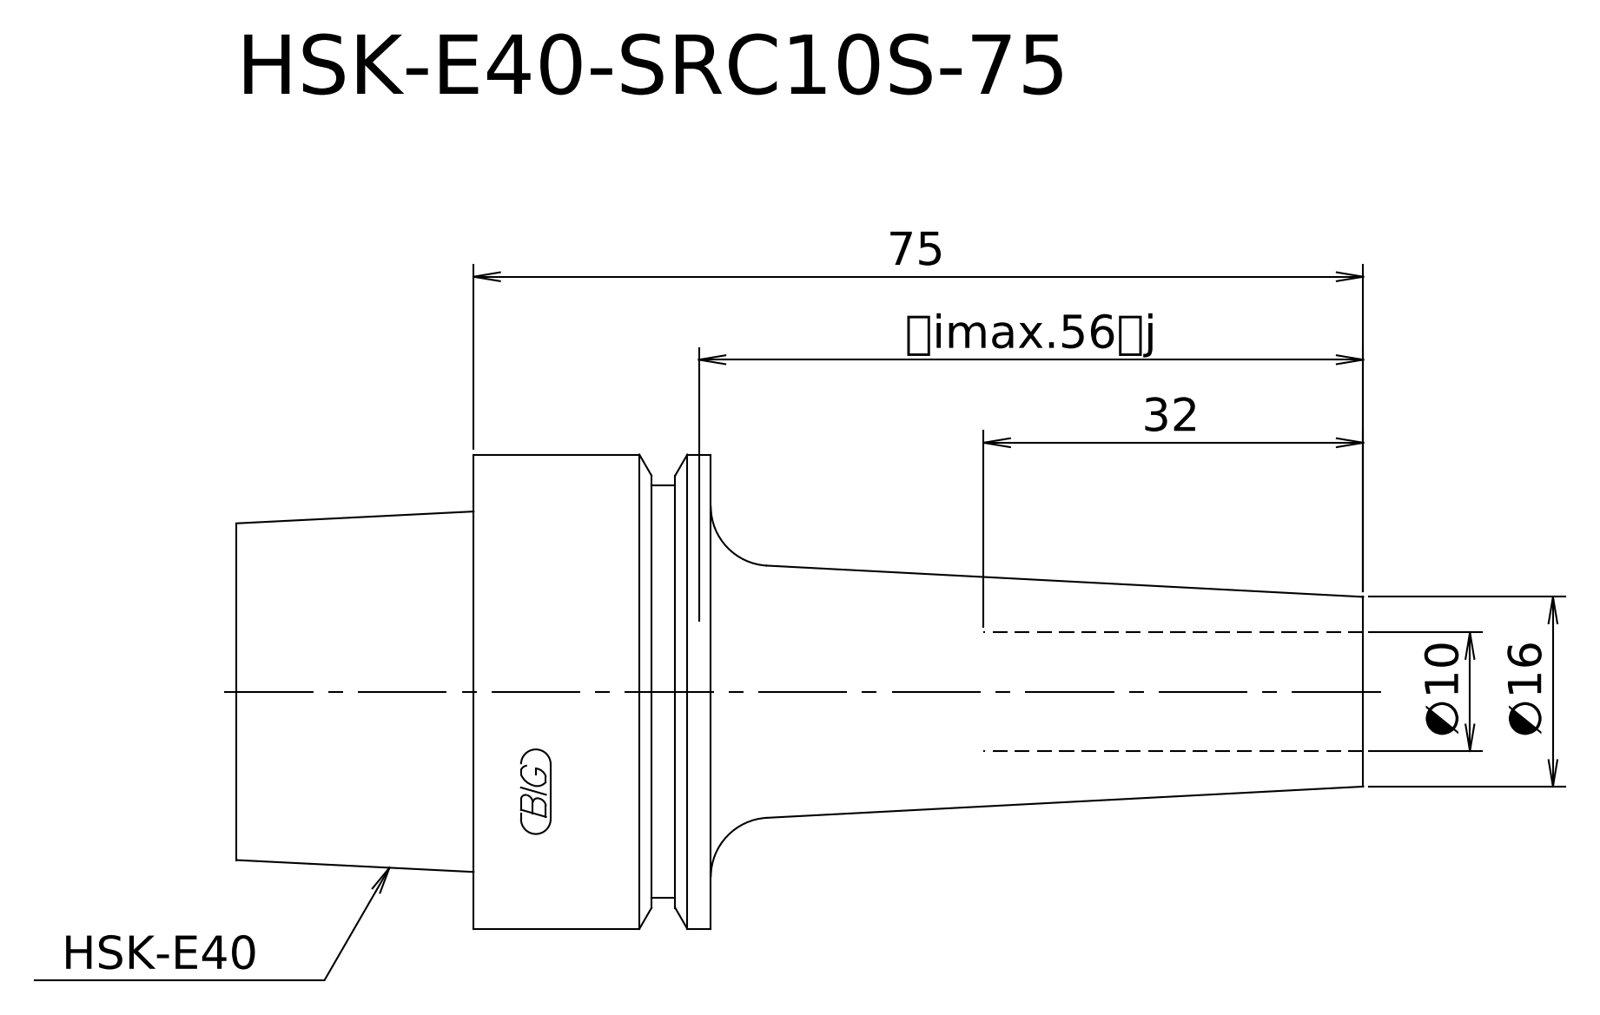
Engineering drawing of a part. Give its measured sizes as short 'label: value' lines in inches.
written by: Kubotek KeyCreator V8.5.1 (14335) (CONFIG_CONTROL_DESIGN)
unit: in
bodies: 1 solid, 15 faces (6 planar, 4 cylindrical, 5 other)
size: 3.74 × 1.575 × 1.575
volume: 3.312 in³; area: 15.7 in²
bosses: 1× ⌀1.575, 1× ⌀1.37, 1× ⌀1.189
face distances: 0.787, 1.575, 2.165, 2.953, 3.74, 2.283, 0.118, 0.669, 1.457, 2.362
